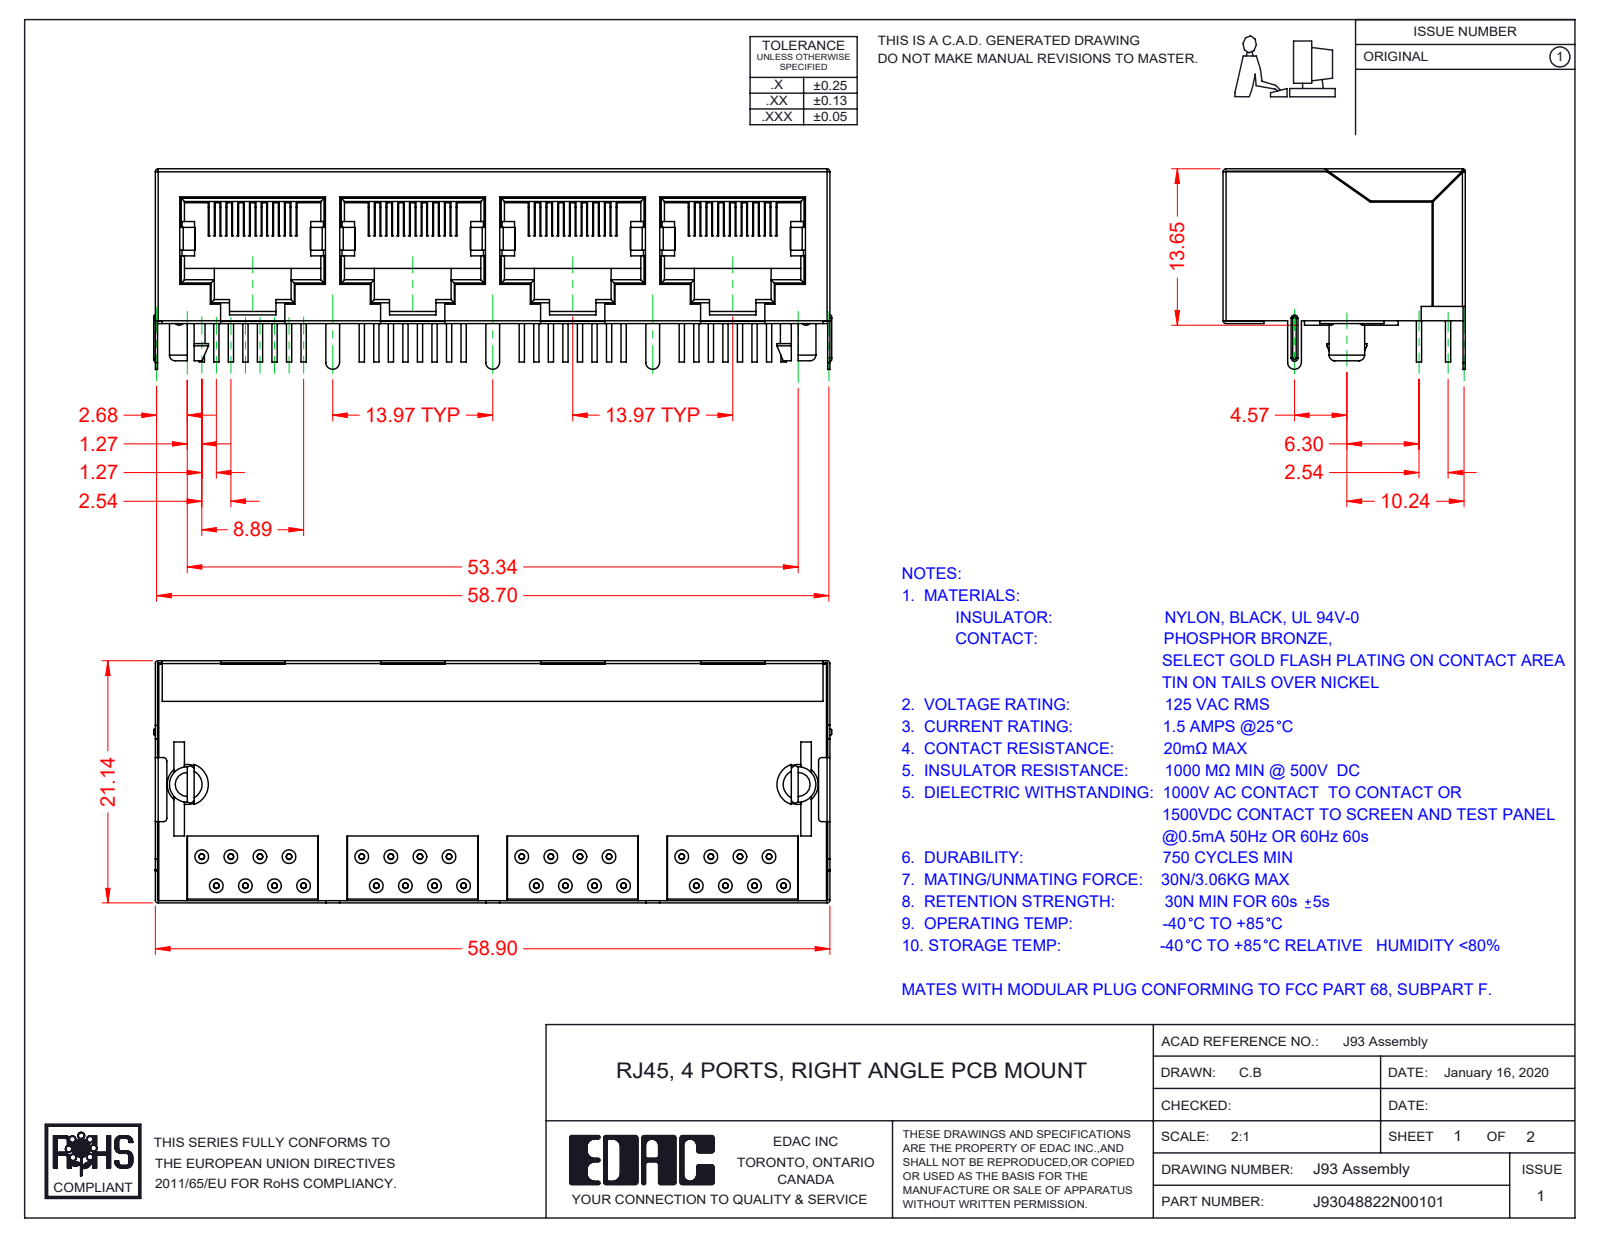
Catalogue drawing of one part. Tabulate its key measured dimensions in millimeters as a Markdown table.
| quantity | value |
| --- | --- |
| part name | 93 Shield; RJ93048822N00101; 93 Contact Lock; 93 Insulator (+1 more) |
| STEP written by | SolidWorks 2016 (CONFIG_CONTROL_DESIGN) |
| units | millimeters |
| bodies | 38 solids, 2070 faces (1065 planar, 665 cylindrical, 340 other) |
| overall size | 59.2 × 21.14 × 17.5 |
| volume | 9 684 mm³ |
| surface area | 21 056 mm² |
| round holes (diameter × count) | 0.46 × 32 |
| round bosses / shafts (diameter × count) | 0.46 × 128, 3.1 × 2 |
| partial cylindrical surfaces (radius × count) | 0.3 × 22, 0.5 × 22, 0.19 × 16, 0.25 × 11, 0.15 × 4, 0.6 × 4, 0.4 × 2, 0.46 × 2 |
| main face-to-face distances | 0.8, 12.25, 12.2, 1, 0.75, 13.25, 13.05, 1.05, 0.85, 13 |
| hole center spacings | 2.84, 2.54, 13.97, 15.45, 12.95, 4.58, 16.51, 11.43 |
